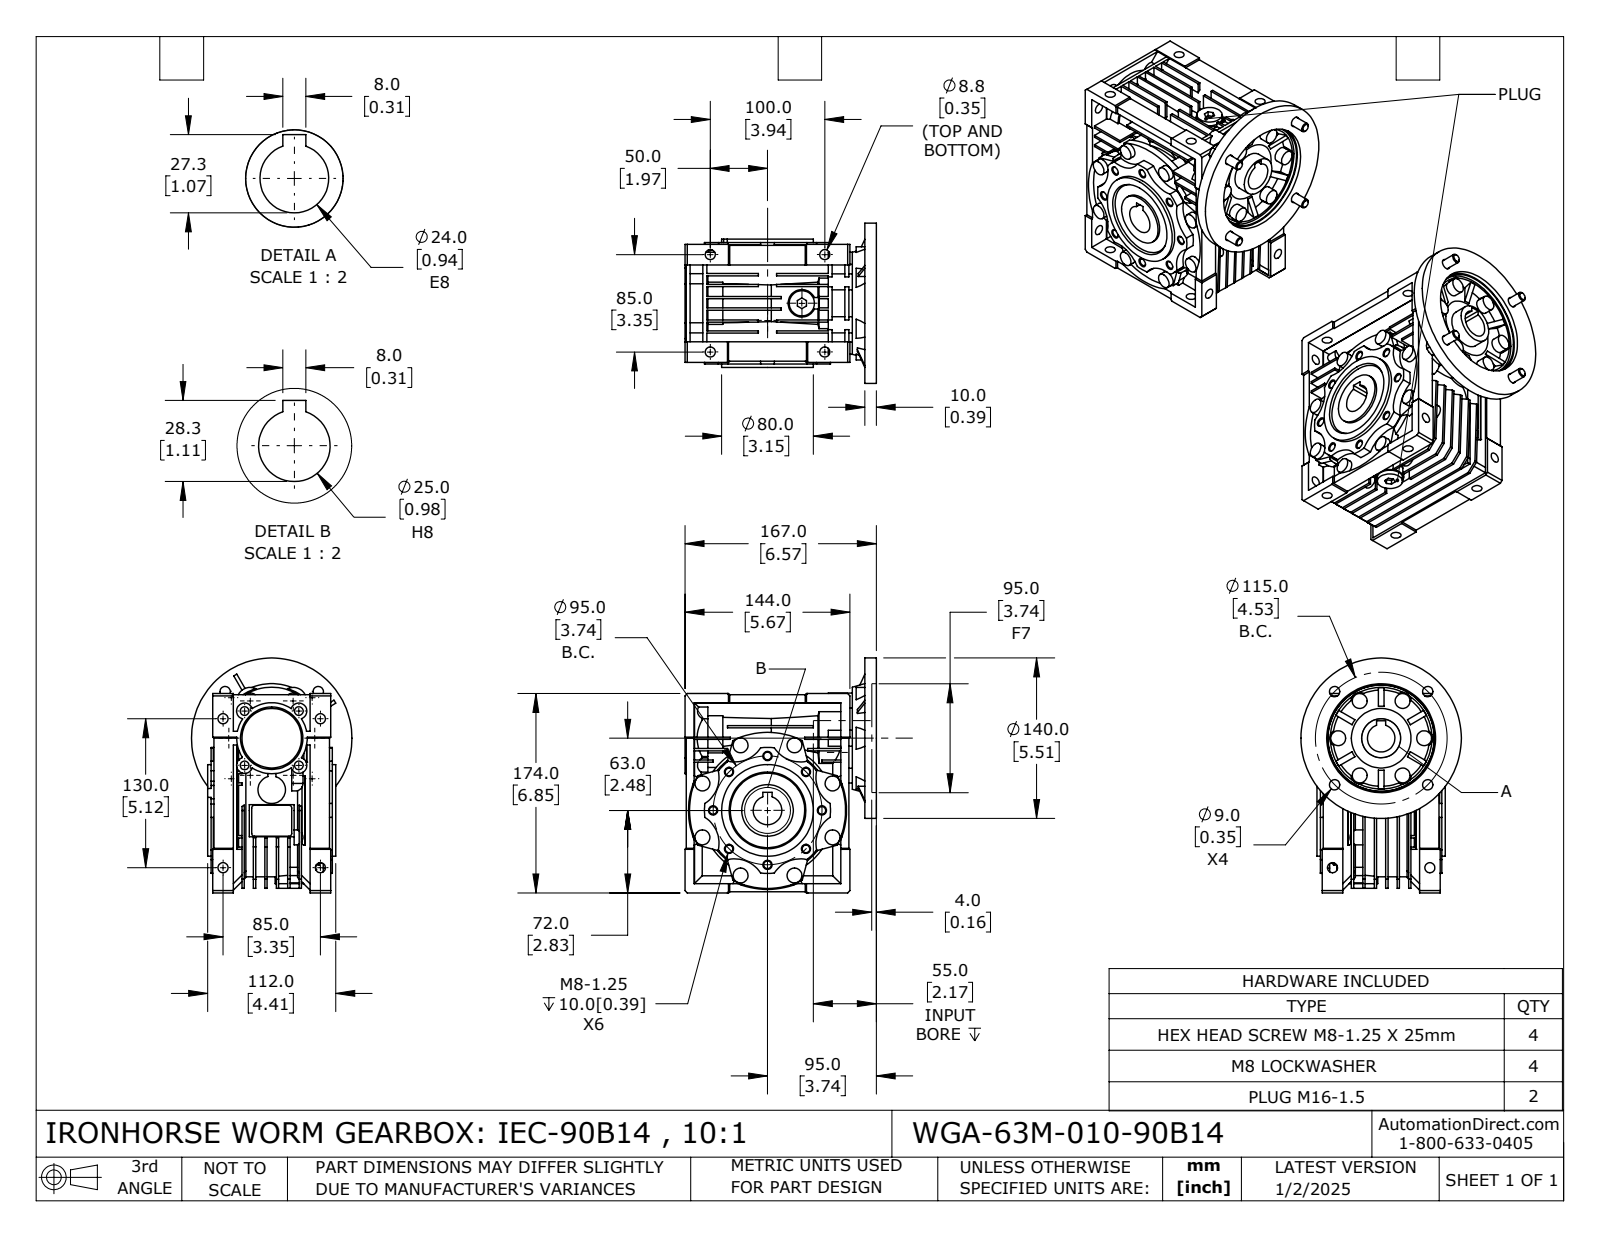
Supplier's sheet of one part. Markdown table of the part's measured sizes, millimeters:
| quantity | value |
| --- | --- |
| part name | WGA-63M-010-90B14 |
| STEP written by | SolidWorks 2024 (CONFIG_CONTROL_DESIGN) |
| units | millimeters |
| bodies | 16 solids, 1375 faces (833 planar, 365 cylindrical, 177 other) |
| overall size | 205 × 180 × 140 |
| volume | 1 870 000 mm³ |
| surface area | 362 276 mm² |
| round holes (diameter × count) | 6.65 × 8, 8.78 × 8, 7.56 × 4, 8.2 × 4, 9 × 4, 14.5 × 2, 25 × 2, 24 × 1, 34 × 1, 37 × 1, 45 × 1, 52 × 1 |
| round bosses / shafts (diameter × count) | 13 × 14, 15.4 × 4, 8 × 4, 24 × 3, 22 × 2, 15.8 × 2, 13.7 × 2, 140 × 1 |
| partial cylindrical surfaces (radius × count) | 7 × 10, 27 × 8, 7.5 × 6, 11.9 × 6, 2.5 × 4, 8.35 × 1, 29.5 × 1, 30.5 × 1 |
| main face-to-face distances | 10, 8, 20, 2, 30, 12, 7, 18, 40, 21 |
| hole center spacings | 36.36, 47.5, 66.55, 67.18, 87.77, 24, 33.5, 47.38 |
